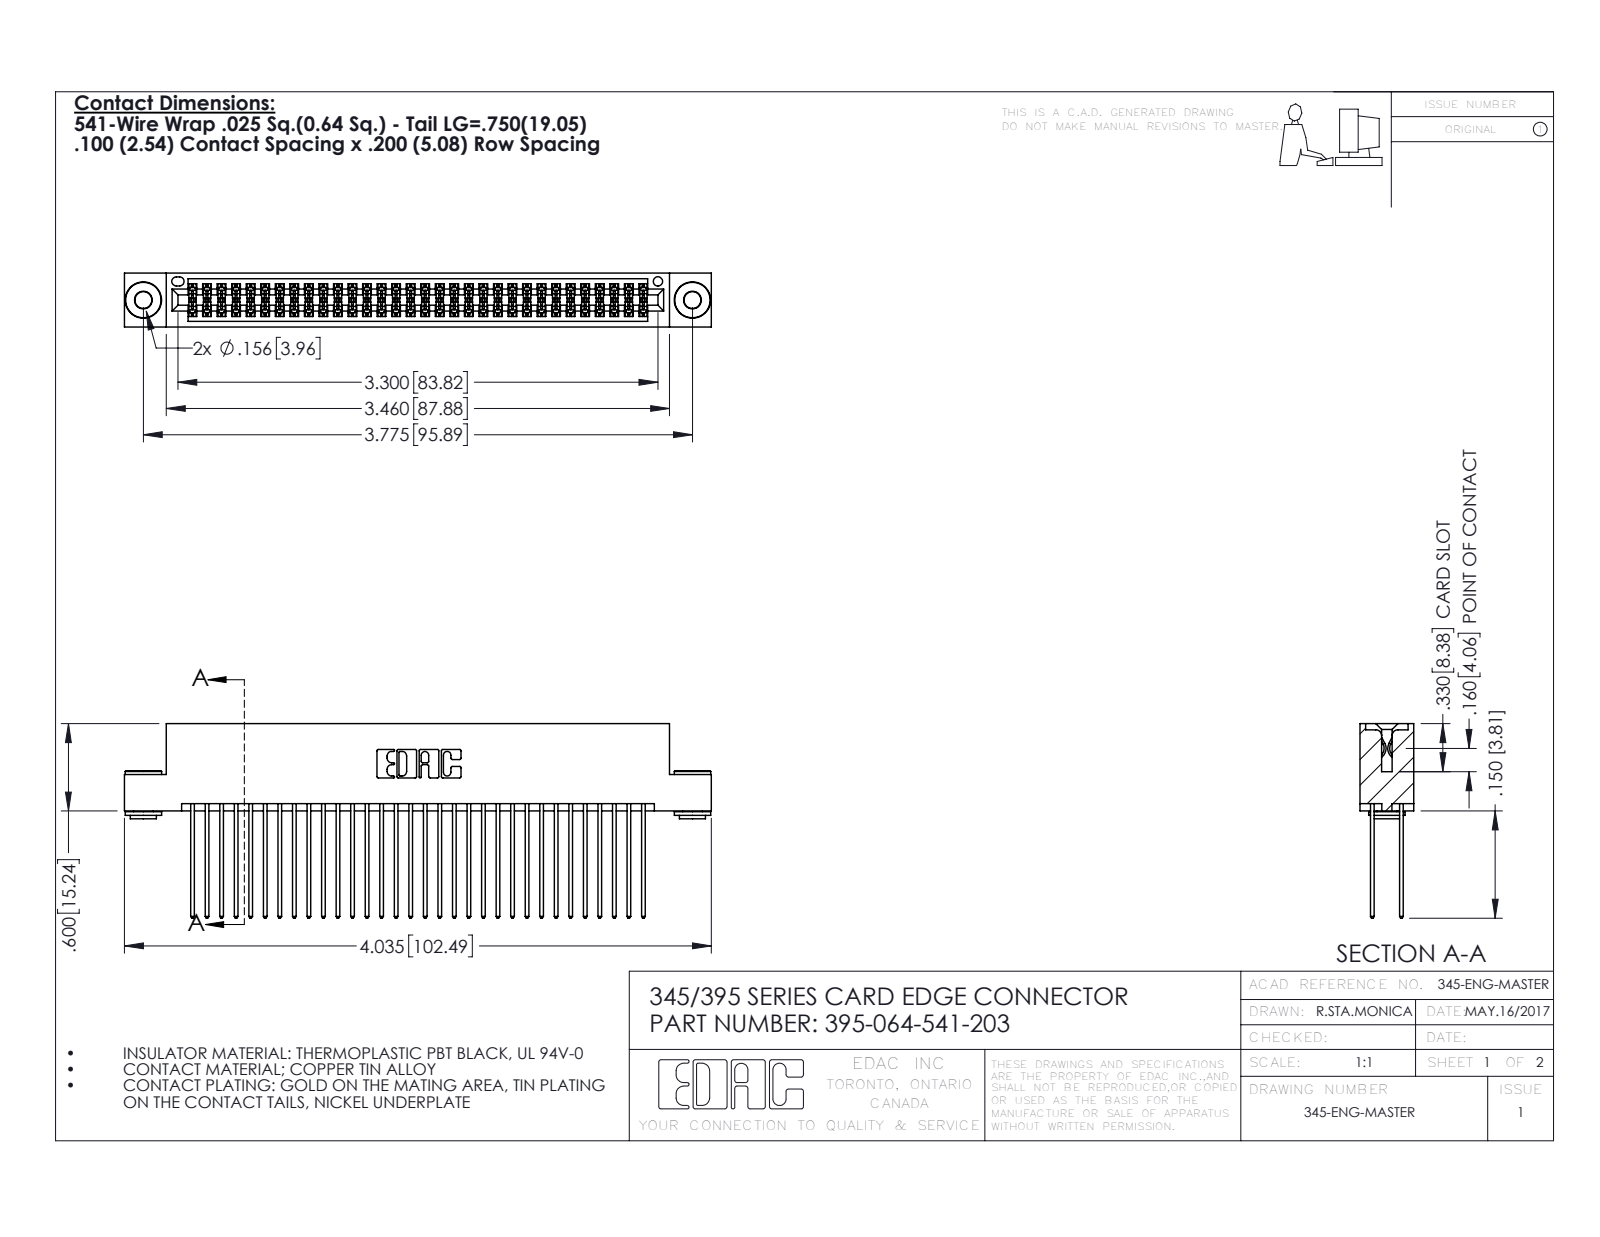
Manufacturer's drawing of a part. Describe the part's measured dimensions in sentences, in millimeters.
The part is named "345-250-002_345-250-002-102; 395-064-541-203; 345-292-001_345-293-141; 345 Part_Flush Mounting Lugs - 0.156 Dia-TH". Its 3-D file was written by "SolidWorks 2016 (CONFIG_CONTROL_DESIGN)". It is 67 solids with 3364 faces: 2202 planar, 1154 cylindrical and 8 other. Overall it measures 102.5 by 34 by 9.4 millimeters. Its volume is 10 200 cubic millimeters and its surface area 16 890 square millimeters. Round holes: 2 of diameter 2.9, 2 of diameter 4, 1 of diameter 1.6. Round bosses or shafts: 2 of diameter 6.4, 2 of diameter 4.6, 2 of diameter 3.5. Partial cylindrical surfaces (rounded edges, fillets, slot ends): 96 of radius 0.2, 64 of radius 0.3, 22 of radius 0.3, 6 of radius 0.2, 6 of radius 0.8, 3 of radius 0.7, 2 of radius 0.4, 2 of radius 0.5. The main face-to-face distances are 1.8, 7.6, 5.1, 0.6, 2.5, 6.9, 5.7, 9.4, 4.4, 3.8. The hole center spacings are 6.9, 89.9, 95.9.
